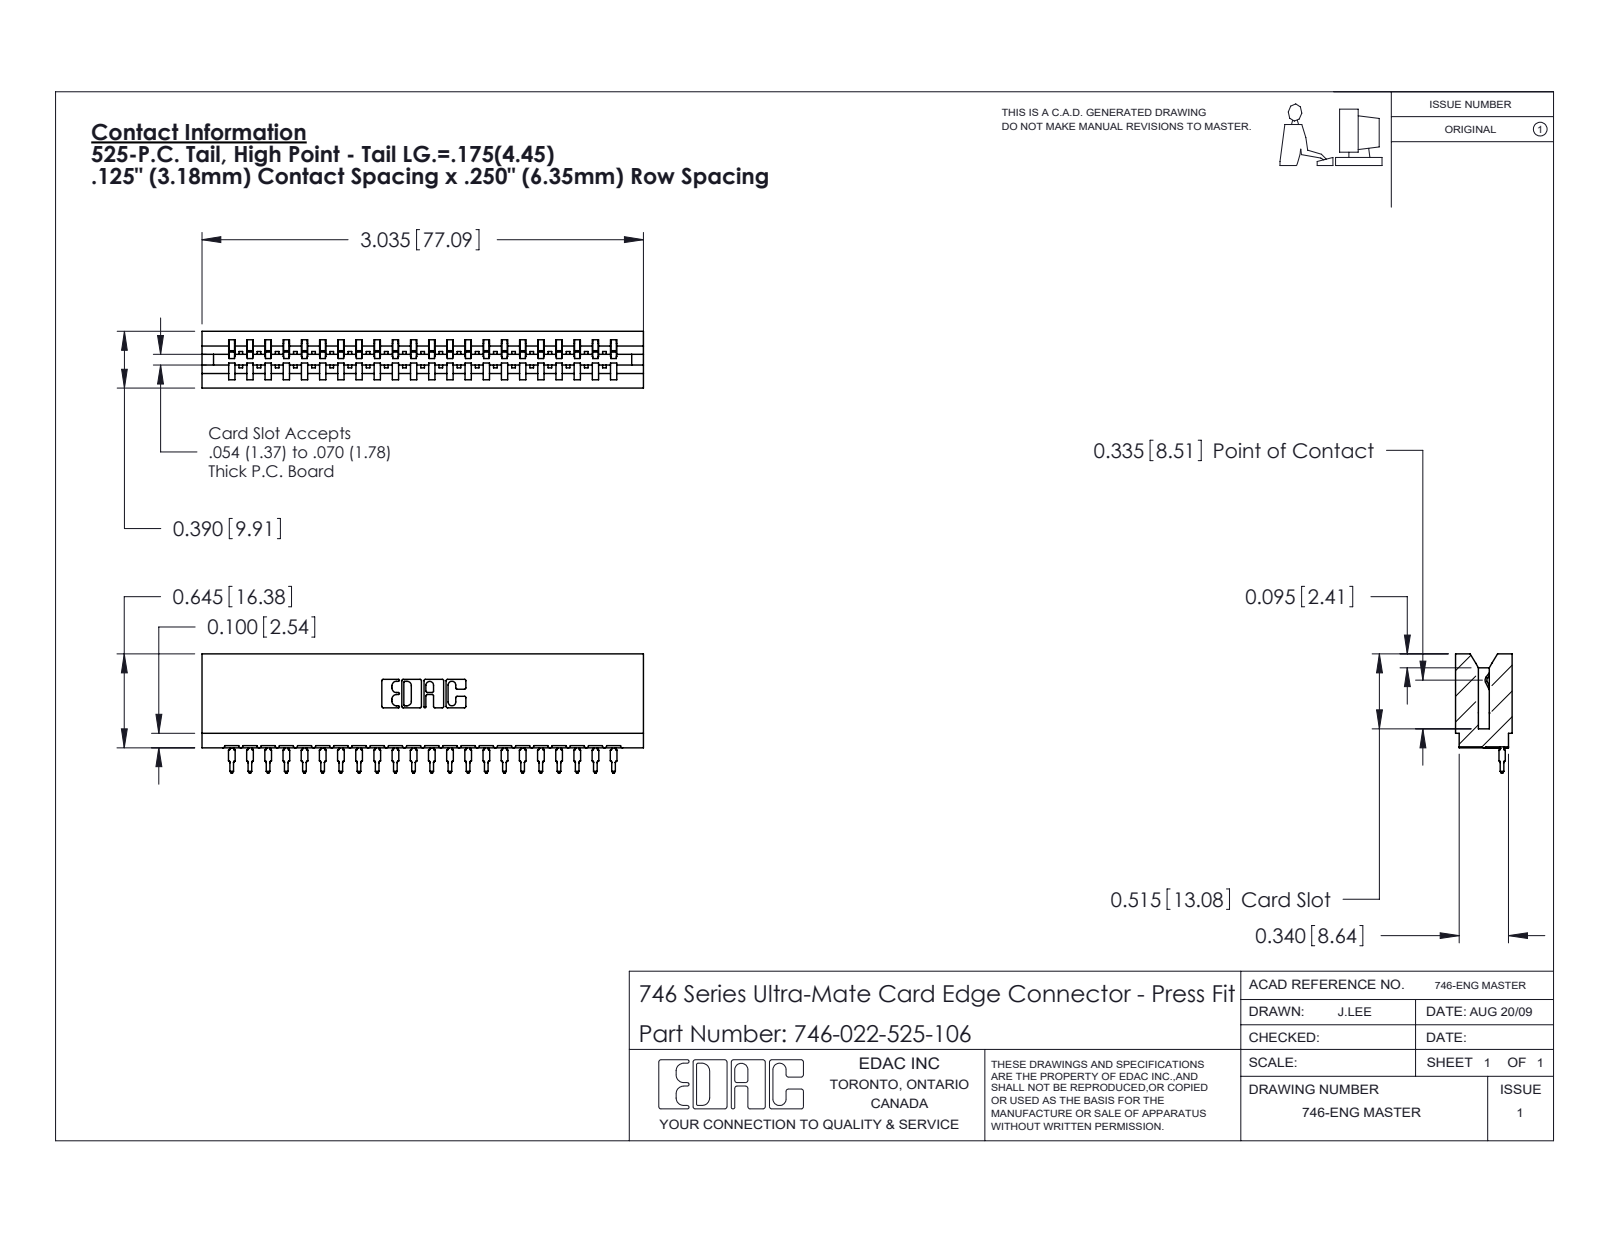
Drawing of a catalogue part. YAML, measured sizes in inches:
part_name: "746 Part_.515 Slot Depth - 06; 746-292-001_525; 746-022-525-106"
step_written_by: "SolidWorks 2020 (CONFIG_CONTROL_DESIGN)"
units: inches
bodies: {solids: 23, faces: 2474, planar: 1442, cylindrical: 460, other: 572}
overall_size: [3.035, 0.819, 0.39]
volume: 0.497
surface_area: 18.04
partial_cylinders:
  - {radius: 0.021, count: 44}
  - {radius: 0.015, count: 23}
  - {radius: 0.01, count: 22}
  - {radius: 0.007, count: 6}
  - {radius: 0.031, count: 6}
  - {radius: 0.005, count: 4}
  - {radius: 0.011, count: 4}
  - {radius: 0.026, count: 3}
face_to_face_distances: [0.333, 0.057, 0.25, 0.39, 0.5, 0.042, 0.025, 0.307, 0.083, 0.125]
